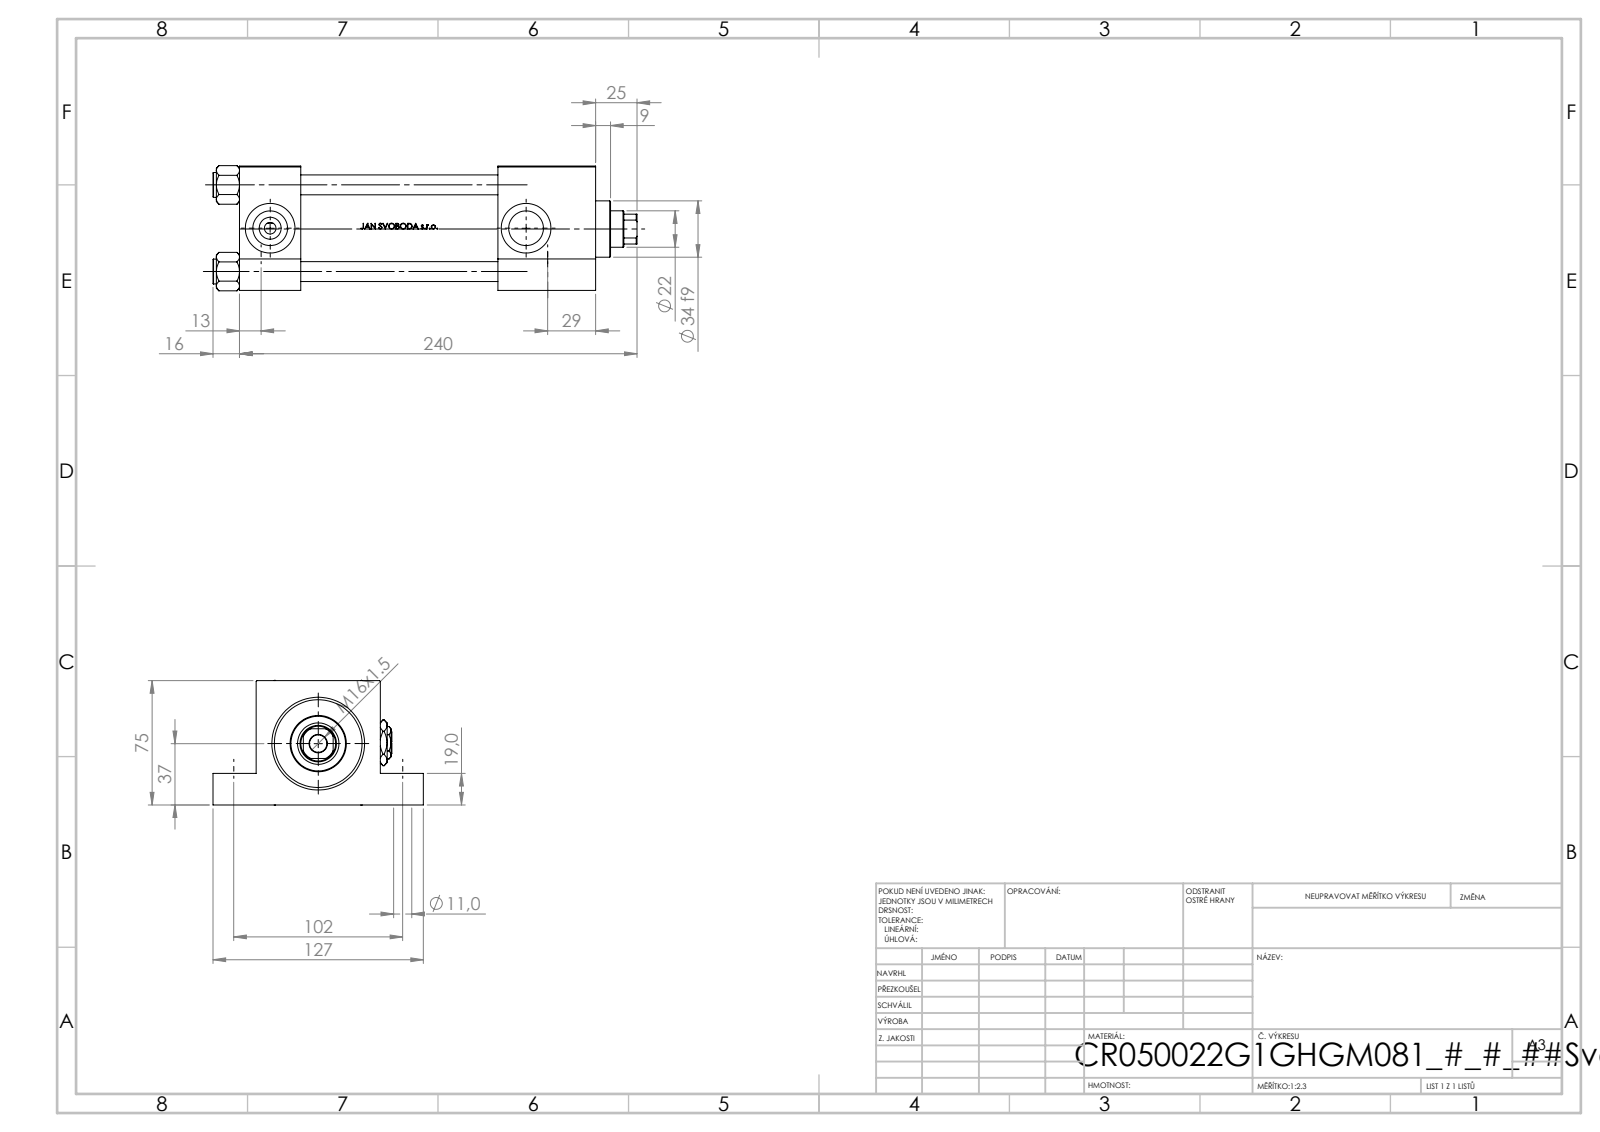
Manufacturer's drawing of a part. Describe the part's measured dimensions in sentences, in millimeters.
The part is named "V215CR_VCP_G; V215CR_G_TYCINKA; V215_VC_A; NUT_M5_G (+2 more)". Its 3-D file was written by "SolidWorks 2019 (CONFIG_CONTROL_DESIGN)". It is 12 solids with 1134 faces: 454 planar, 128 cylindrical and 552 other. Overall it measures 256 by 127 by 75.54 millimeters. Its volume is 833 657 cubic millimeters and its surface area 195 032 square millimeters. Round holes: 4 of diameter 11, 4 of diameter 12, 2 of diameter 7, 2 of diameter 20.96, 2 of diameter 30, 1 of diameter 10.5, 1 of diameter 22, 1 of diameter 25, 1 of diameter 41, 1 of diameter 50, 1 of diameter 53. Round bosses or shafts: 4 of diameter 15, 1 of diameter 56, 1 of diameter 34. Partial cylindrical surfaces (rounded edges, fillets, slot ends): 1 of radius 10.5. The main face-to-face distances are 75, 37, 215, 178, 19, 56, 156, 119, 59, 26. The hole center spacings are 52.3, 36.63, 37.34, 73.96, 102, 173, 200.83, 154.5.
